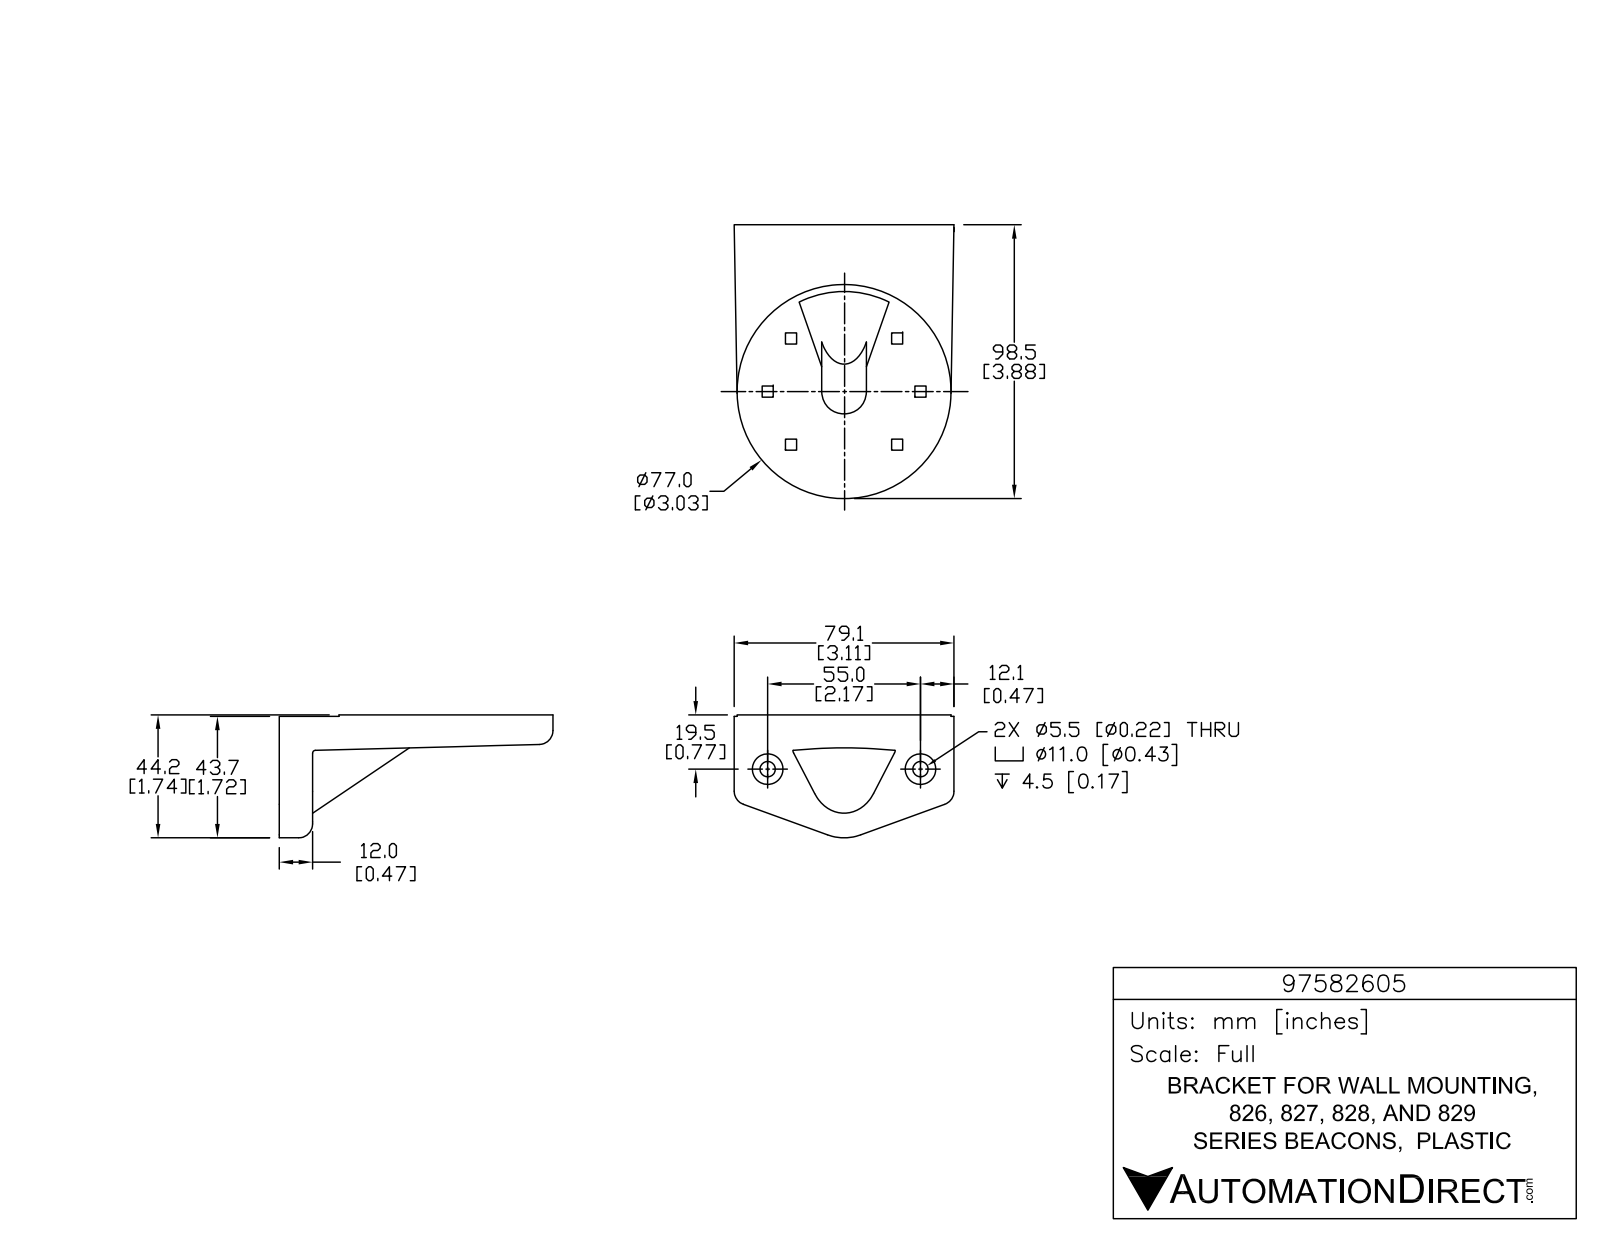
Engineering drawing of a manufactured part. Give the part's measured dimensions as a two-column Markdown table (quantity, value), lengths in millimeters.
| quantity | value |
| --- | --- |
| part name | 97582605 |
| STEP written by | SolidWorks 2017 (AUTOMOTIVE_DESIGN) |
| units | millimeters |
| bodies | 1 solid, 838 faces (616 planar, 214 cylindrical, 8 other) |
| overall size | 98.6 × 79.3 × 44.2 |
| volume | 84 440 mm³ |
| surface area | 25 600 mm² |
| round holes (diameter × count) | 1 × 2, 5.5 × 2, 11 × 2, 0.8 × 1 |
| round bosses / shafts (diameter × count) | 5.7 × 2, 1.4 × 2, 77 × 1, 4.9 × 1, 1.2 × 1 |
| partial cylindrical surfaces (radius × count) | 5 × 8, 0.2 × 4, 0.2 × 4, 0.2 × 4, 3.3 × 4, 0.1 × 2, 0.1 × 2, 0.2 × 2 |
| main face-to-face distances | 0.5, 3, 3.5, 12, 4, 5.5, 6, 2.5, 19.1, 38.2 |
| hole center spacings | 27.1, 35.8, 55 |
